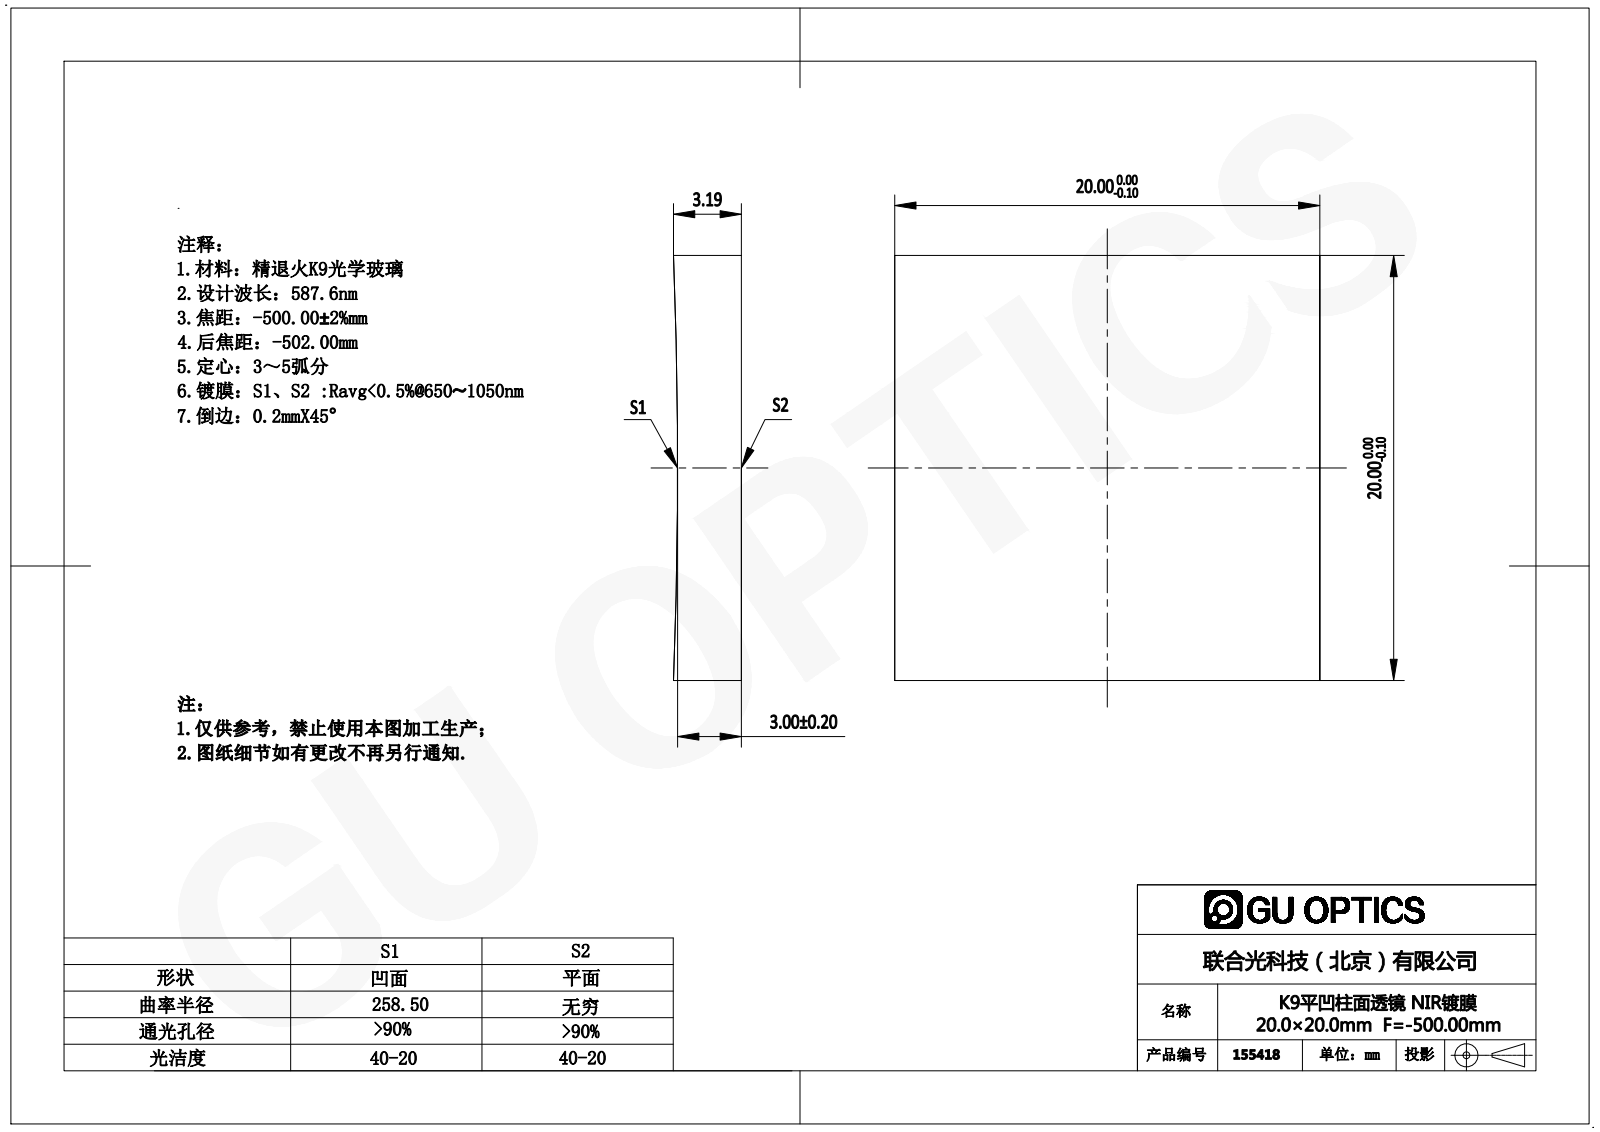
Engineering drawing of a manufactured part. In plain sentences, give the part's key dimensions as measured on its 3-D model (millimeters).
The part is named "155352". Its 3-D file was written by "SolidWorks 2016 (AUTOMOTIVE_DESIGN)". It is 1 solid with 6 faces: 5 planar, 1 cylindrical and 0 other. Overall it measures 20 by 20 by 3.19 millimeters. Its volume is 1 226 cubic millimeters and its surface area 1 050 square millimeters. Partial cylindrical surfaces (rounded edges, fillets, slot ends): 1 of radius 258.5. The main face-to-face distances are 20.
